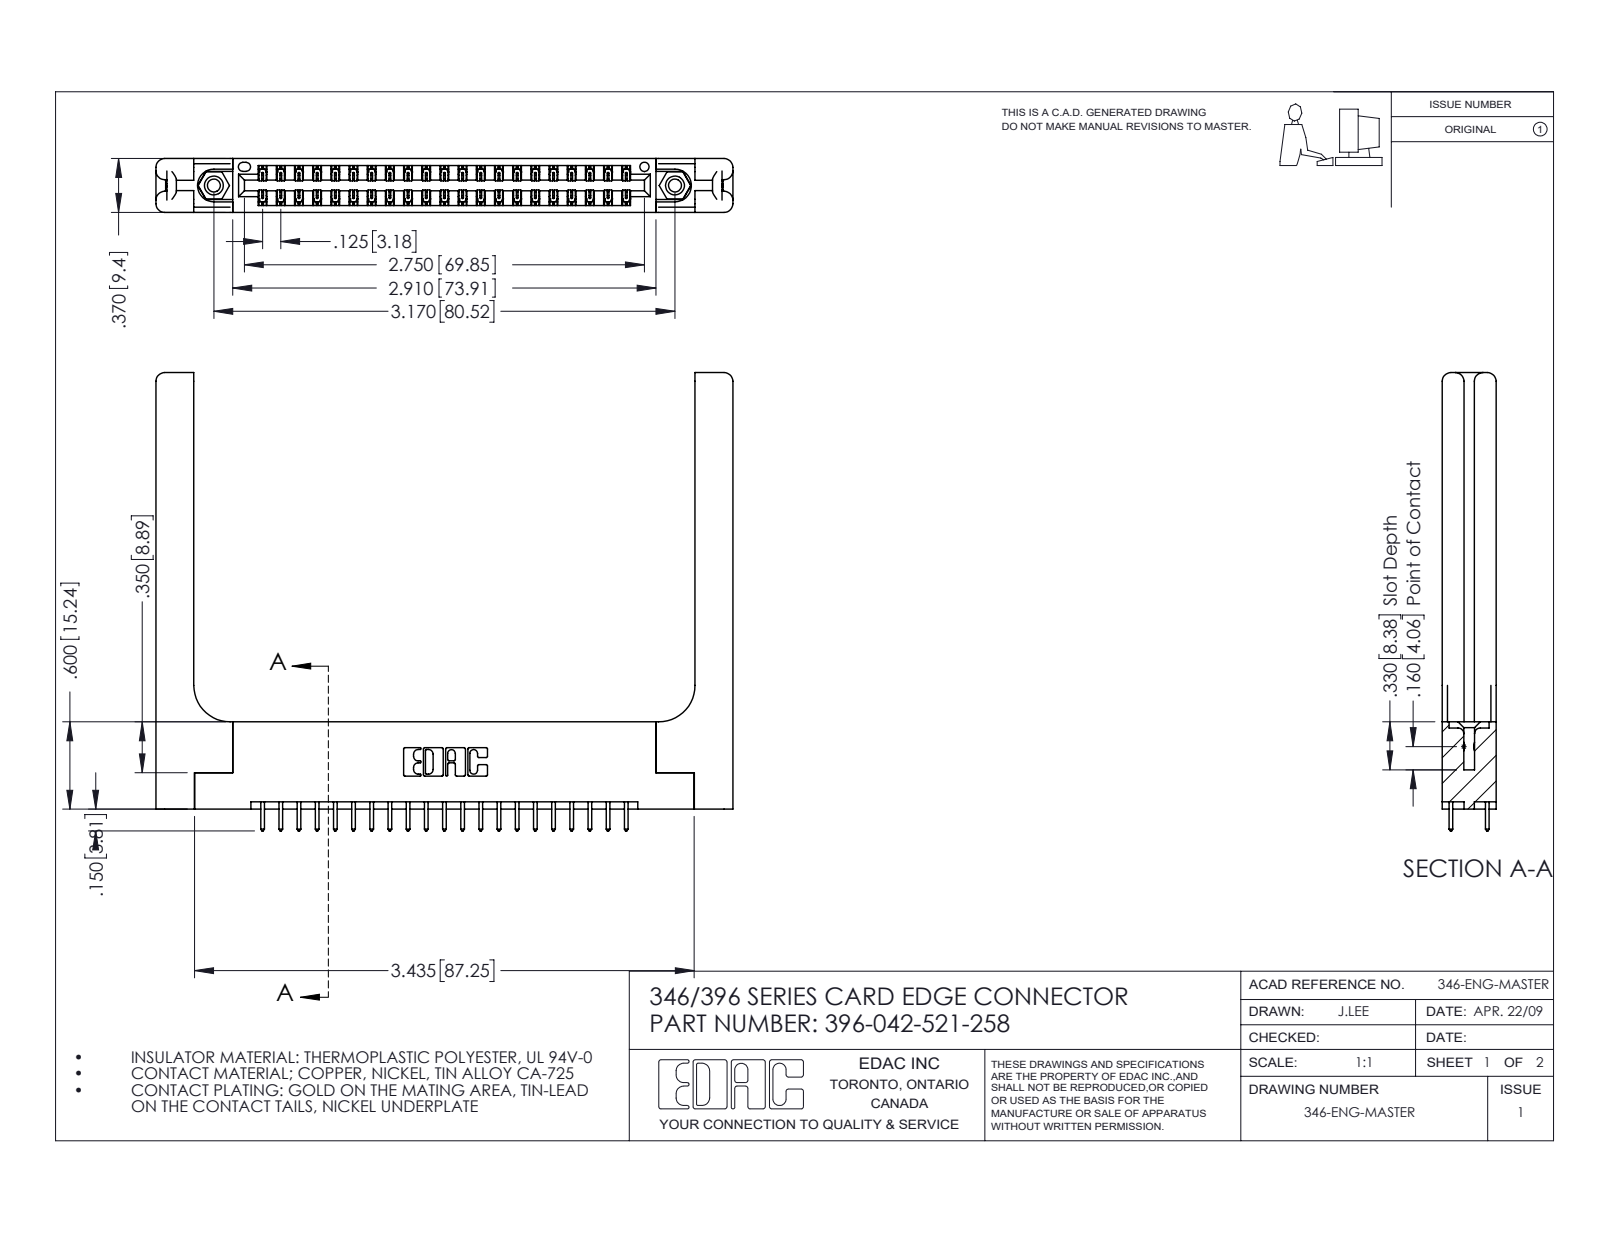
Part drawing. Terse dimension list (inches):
name: 345-292-001_345-293-121; 345-250-001_345-250-001-102; 346 Part_Flush Mounting Lugs - 0.156 Dia-TH; 346-220-058_345-220-058 (+1 more)
written by: SolidWorks 2016 (CONFIG_CONTROL_DESIGN)
unit: in
bodies: 47 solids, 2562 faces (1694 planar, 808 cylindrical, 60 other)
size: 3.966 × 3.15 × 0.37
volume: 1.046 in³; area: 27.56 in²
holes: 2× ⌀0.089, 2× ⌀0.125, 2× ⌀0.156, 1× ⌀0.064
bosses: 2× ⌀0.155
rounds: 63× R0.006, 42× R0.01, 22× R0.01, 16× R0.06, 6× R0.007, 6× R0.031, 3× R0.026, 2× R0.014
face distances: 0.37, 0.072, 0.048, 0.322, 0.148, 0.15, 0.25, 0.025, 0.298, 0.077
hole spacings: 0.246, 2.963, 3.17
